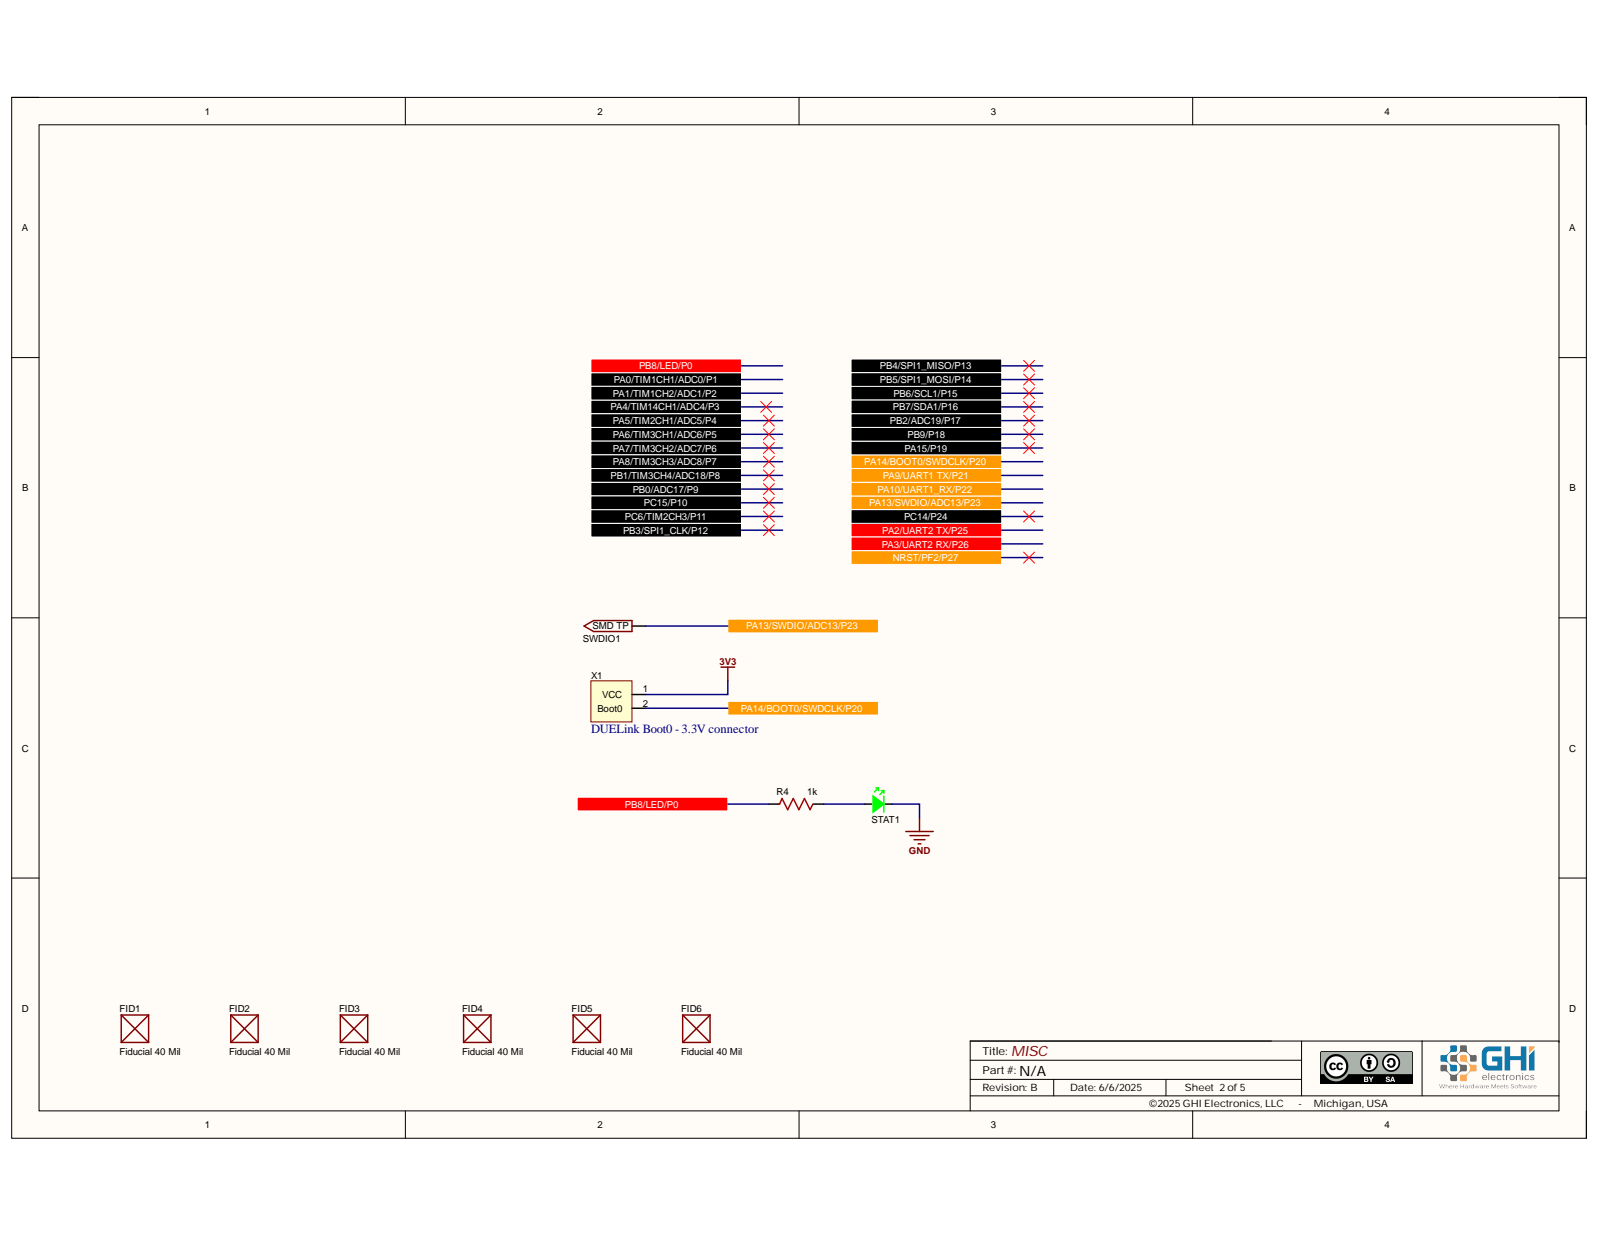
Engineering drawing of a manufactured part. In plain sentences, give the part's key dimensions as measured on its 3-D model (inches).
The part is named "PCB; Board; C3; C0402 (+6 more)". Its 3-D file was written by "Open CASCADE 7.5 (AUTOMOTIVE_DESIGN)". It is 108 solids with 1998 faces: 1207 planar, 437 cylindrical and 354 other. Overall it measures 1.85 by 1.654 by 0.591 inches. Its volume is 0.277 cubic inches and its surface area 16.04 square inches. Round holes: 4 of diameter 0.118, 2 of diameter 0.04, 1 of diameter 0.787, 1 of diameter 0.906, 1 of diameter 0.926, 1 of diameter 0.984, 1 of diameter 0.993. Round bosses or shafts: 4 of diameter 0.039, 1 of diameter 0.978, 1 of diameter 0.911, 1 of diameter 0.852, 1 of diameter 0.63. Partial cylindrical surfaces (rounded edges, fillets, slot ends): 35 of radius 0.005, 26 of radius 0.006, 4 of radius 0.138, 2 of radius 0.007, 2 of radius 0.007, 2 of radius 0.007, 1 of radius 0.004. The main face-to-face distances are 0.039, 0.079, 0.315, 0.118, 0.047, 0.197, 0.472, 0.276, 0.236, 0.425. The hole center spacings are 1.046, 1.378, 1.575, 2.093, 0.1, 0.561, 0.661, 0.719.
